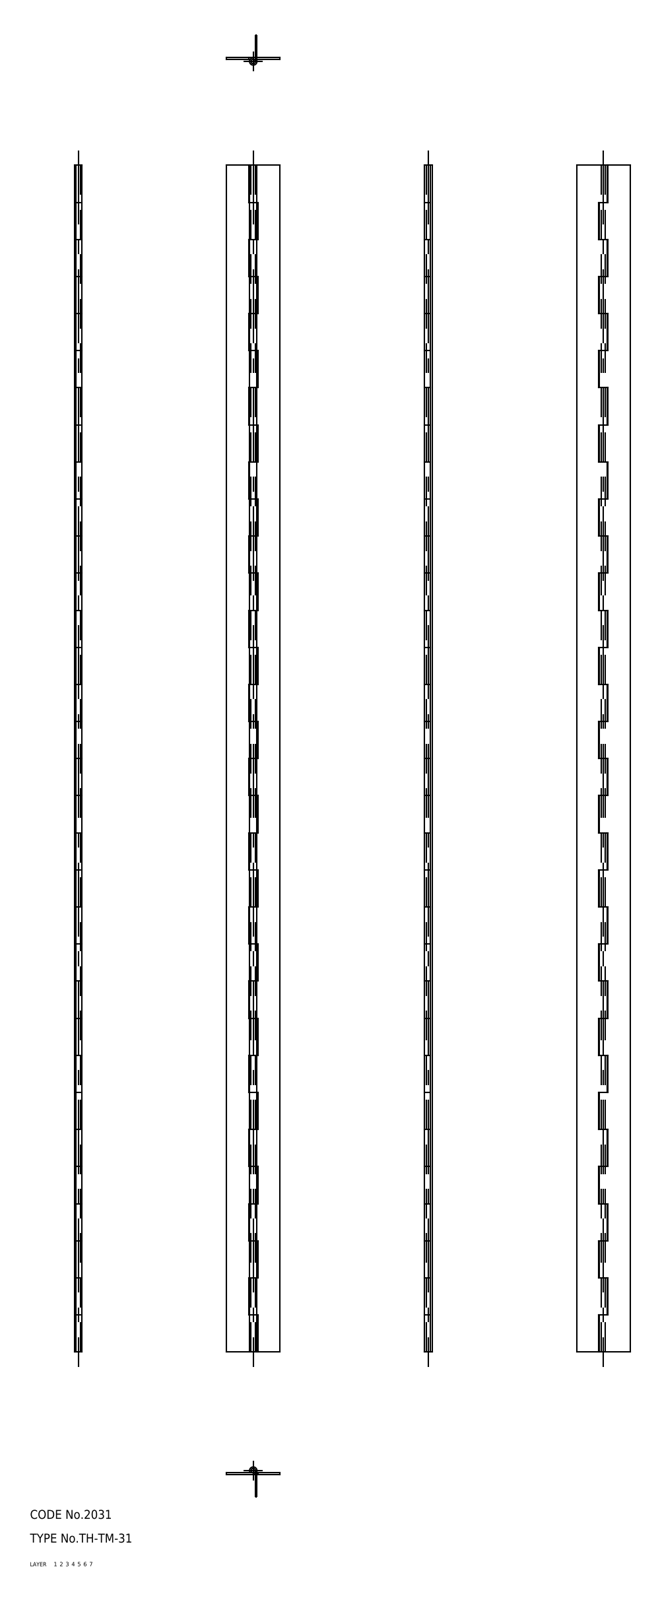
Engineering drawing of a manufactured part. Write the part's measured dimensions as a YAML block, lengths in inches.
part_name: "hinge piece_B; hinge piece_A; shaft; TH_TM_31_22568_36"
step_written_by: "CADfix (AUTOMOTIVE_DESIGN)"
units: inches
bodies: {solids: 3, faces: 204, planar: 0, cylindrical: 0, other: 204}
overall_size: [15.748, 0.709, 0.098]
volume: 0.308
surface_area: 31.45
